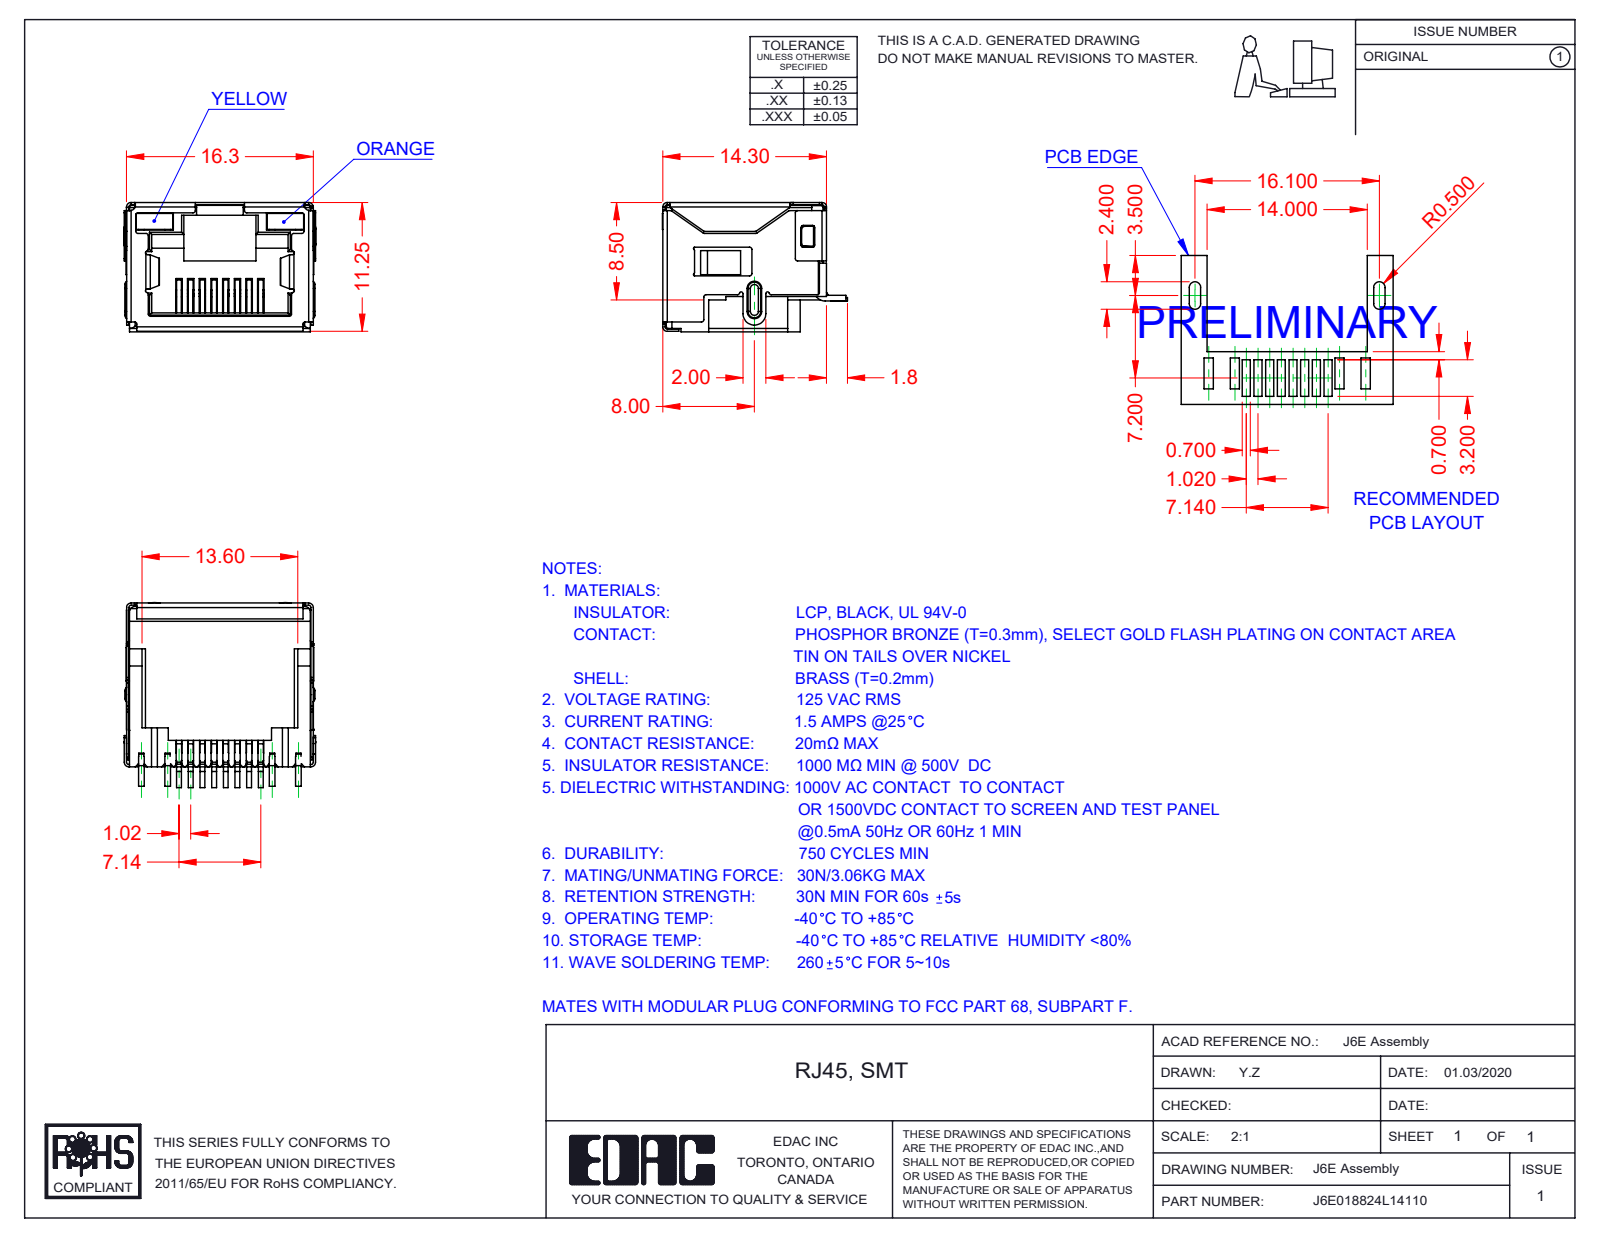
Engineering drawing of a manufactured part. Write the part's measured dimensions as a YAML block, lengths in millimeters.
part_name: "J6E018824L14110; 6E LED RH_4-Orange; 6E Shield_LED; 6E Contacts (+2 more)"
step_written_by: "SolidWorks 2016 (CONFIG_CONTROL_DESIGN)"
units: millimeters
bodies: {solids: 12, faces: 1496, planar: 1099, cylindrical: 347, other: 50}
overall_size: [16.75, 16.15, 11.3]
volume: 1109
surface_area: 4045
partial_cylinders:
  - {radius: 0.2, count: 82}
  - {radius: 0.25, count: 17}
  - {radius: 0.4, count: 13}
  - {radius: 0.5, count: 13}
  - {radius: 0.1, count: 10}
  - {radius: 0.15, count: 7}
  - {radius: 0.3, count: 4}
  - {radius: 1, count: 3}
face_to_face_distances: [11.05, 16.05, 16.1, 15.85, 11.1, 11.3, 2.4, 0.7, 9.85, 0.49]
